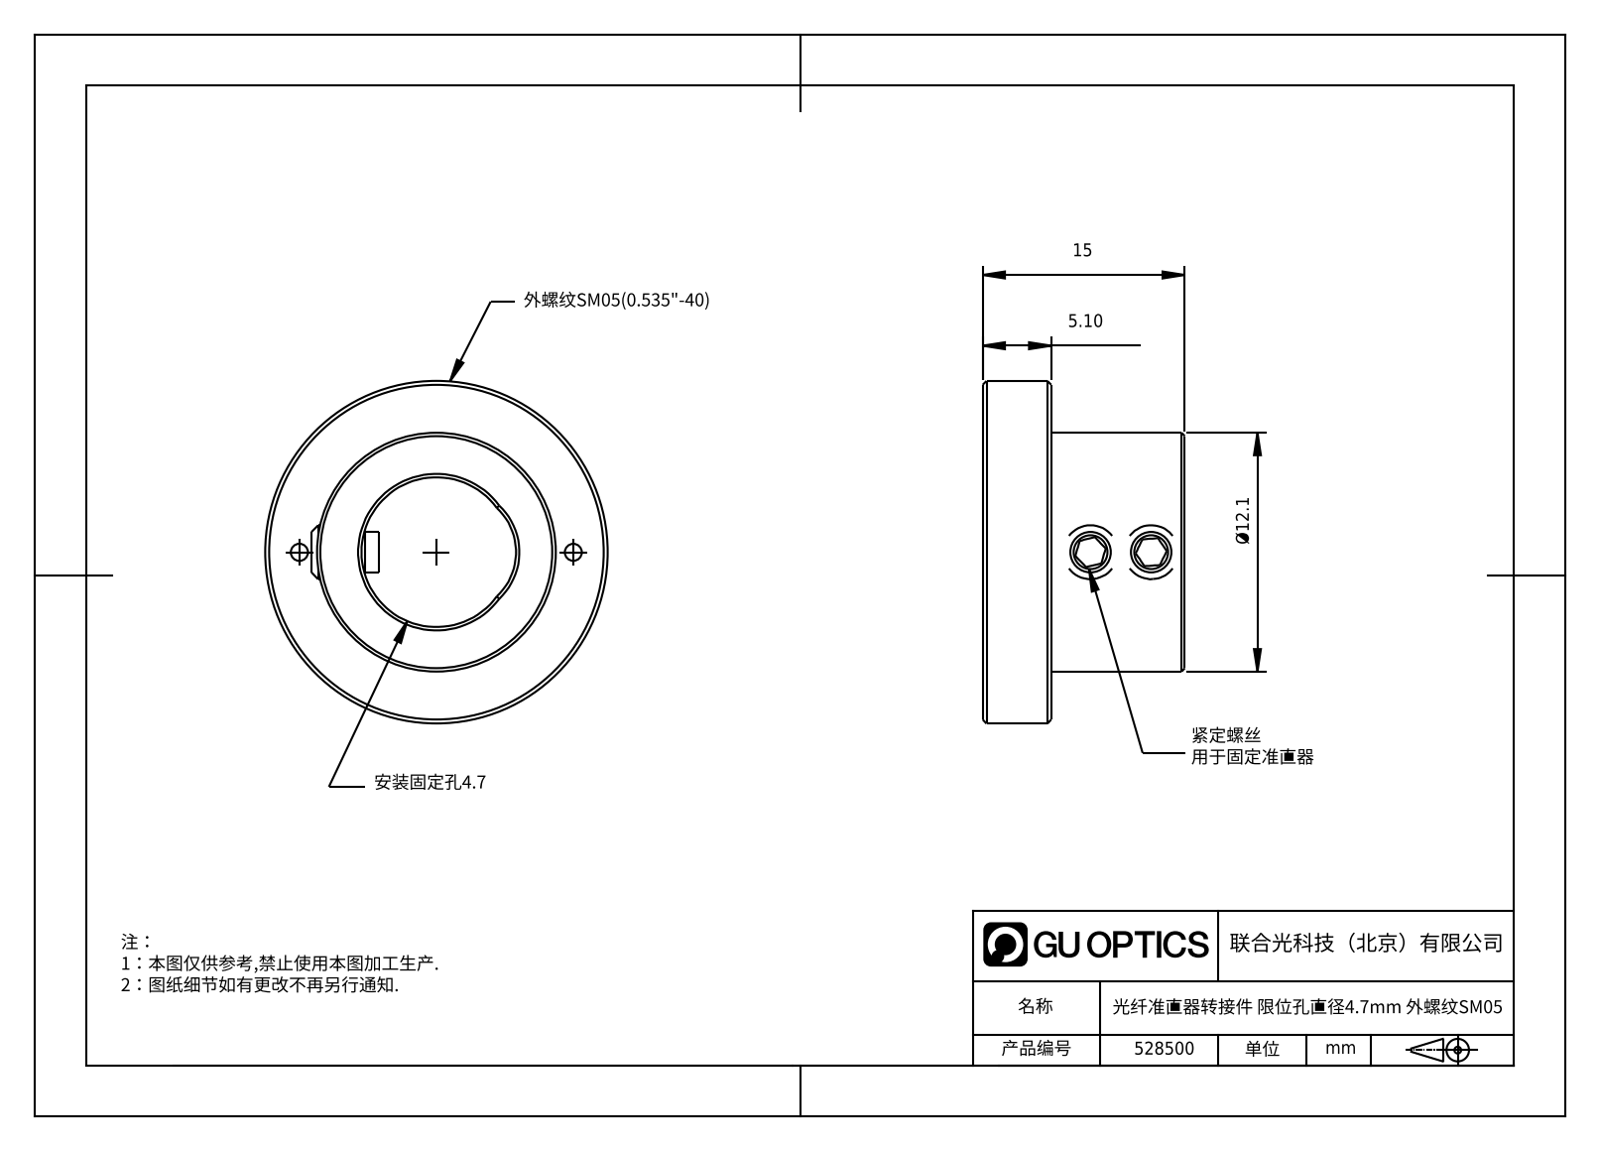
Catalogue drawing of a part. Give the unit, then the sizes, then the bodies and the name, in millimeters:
Units: millimetres
Overall size (bounding box): 15 × 13.59 × 13.59
Round holes (diameter × count): ⌀1.27 ×4, ⌀2.5 ×2, ⌀4.7 ×1
Round bosses / shafts (diameter × count): ⌀4 ×2, ⌀3 ×2, ⌀13.59 ×1, ⌀12.1 ×1
Partial cylindrical surfaces — rounded edges, fillets, slot ends (radius × count): R1.21 ×1
Main face-to-face distances: 15, 5.08, 9.92, 3, 2, 4, 1, 13.8, 8.72, 1.2
Hole centre spacings: 1.7, 3.8, 5.5, 9.3, 4.92, 7.6, 11
Volume: 1 641 mm³ · Surface area: 1 245 mm²
Bodies: 3 solids, 54 faces (25 planar, 14 cylindrical, 15 other)
Part name (STEP PRODUCT): 528500
STEP written by: SolidWorks 2020 (CONFIG_CONTROL_DESIGN)
